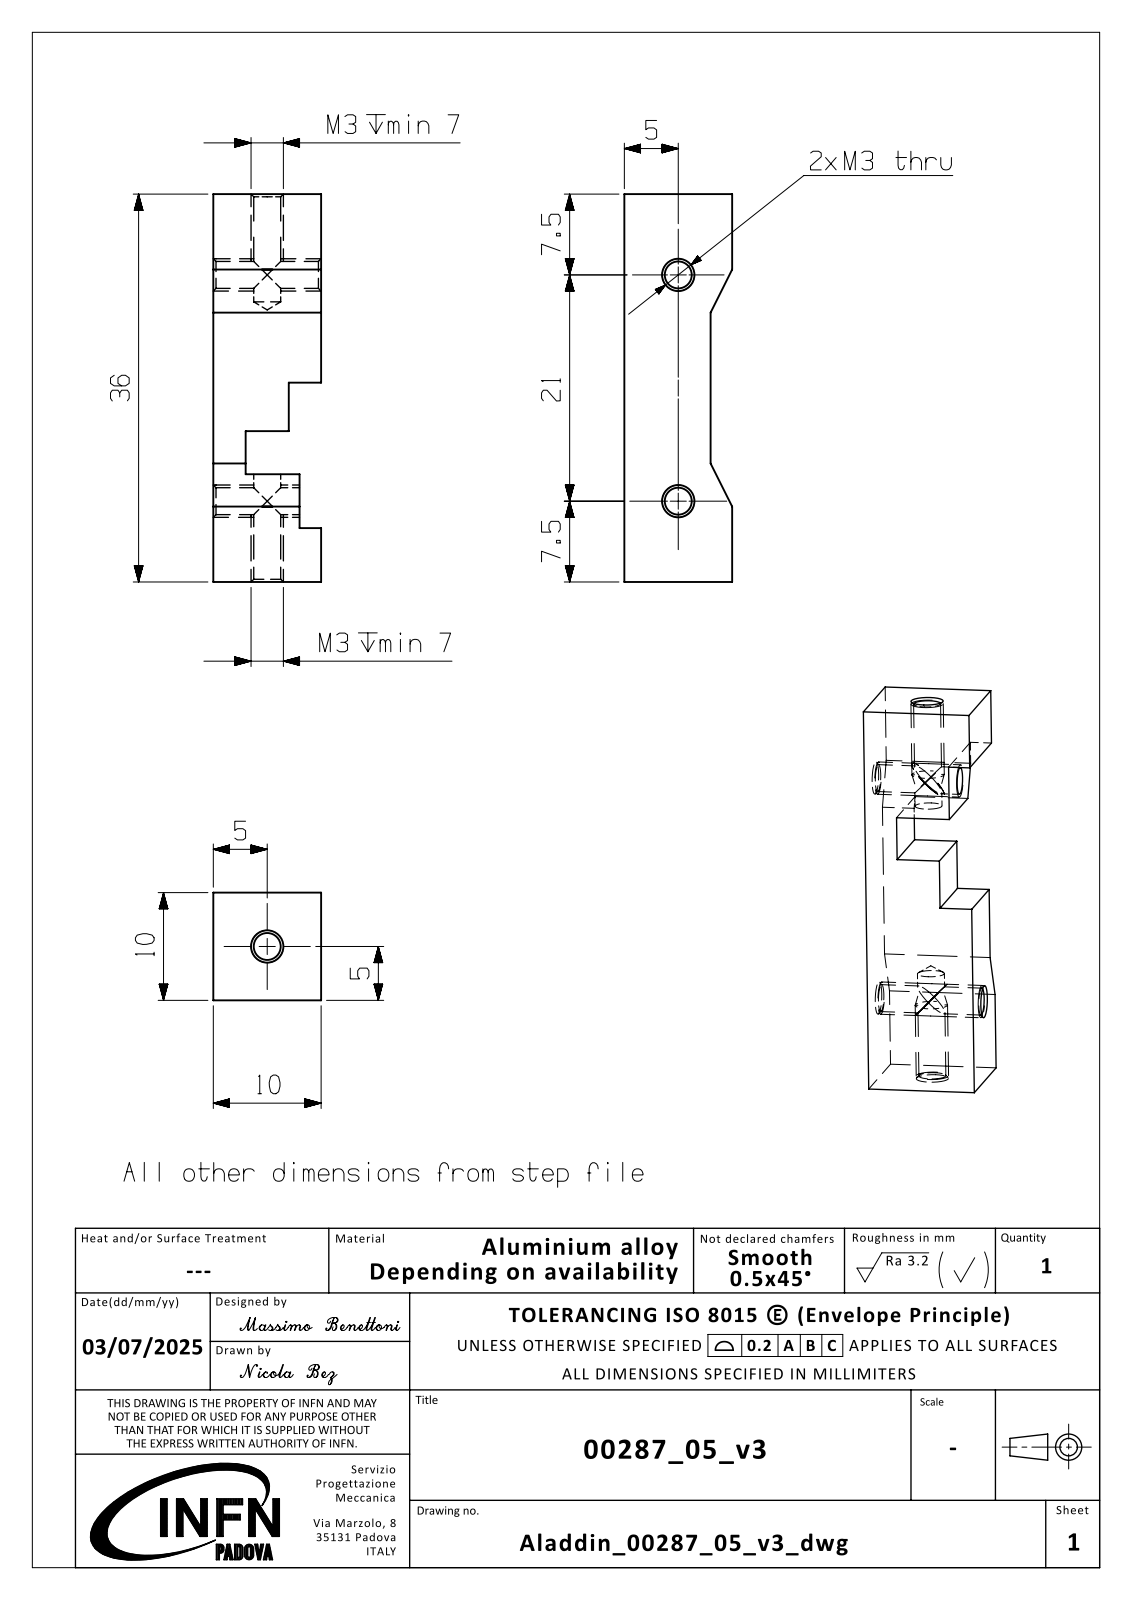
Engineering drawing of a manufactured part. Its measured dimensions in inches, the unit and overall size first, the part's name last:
Units: inches
Overall size (bounding box): 1.417 × 0.394 × 0.394
Round holes (diameter × count): ⌀0.079 ×3
Main face-to-face distances: 0.394, 0.079, 0.315, 1.417, 0.197, 0.118, 0.276, 0.157, 1.024, 0.039
Hole centre spacings: 0.827
Volume: 0.165 in³ · Surface area: 2.753 in²
Bodies: 1 solid, 32 faces (18 planar, 8 cylindrical, 6 other)
Part name (STEP PRODUCT): 00287_05_v3_objects
STEP written by: SIEMENS PLM Software NX2306.9102 (AUTOMOTIVE_DESIGN)
